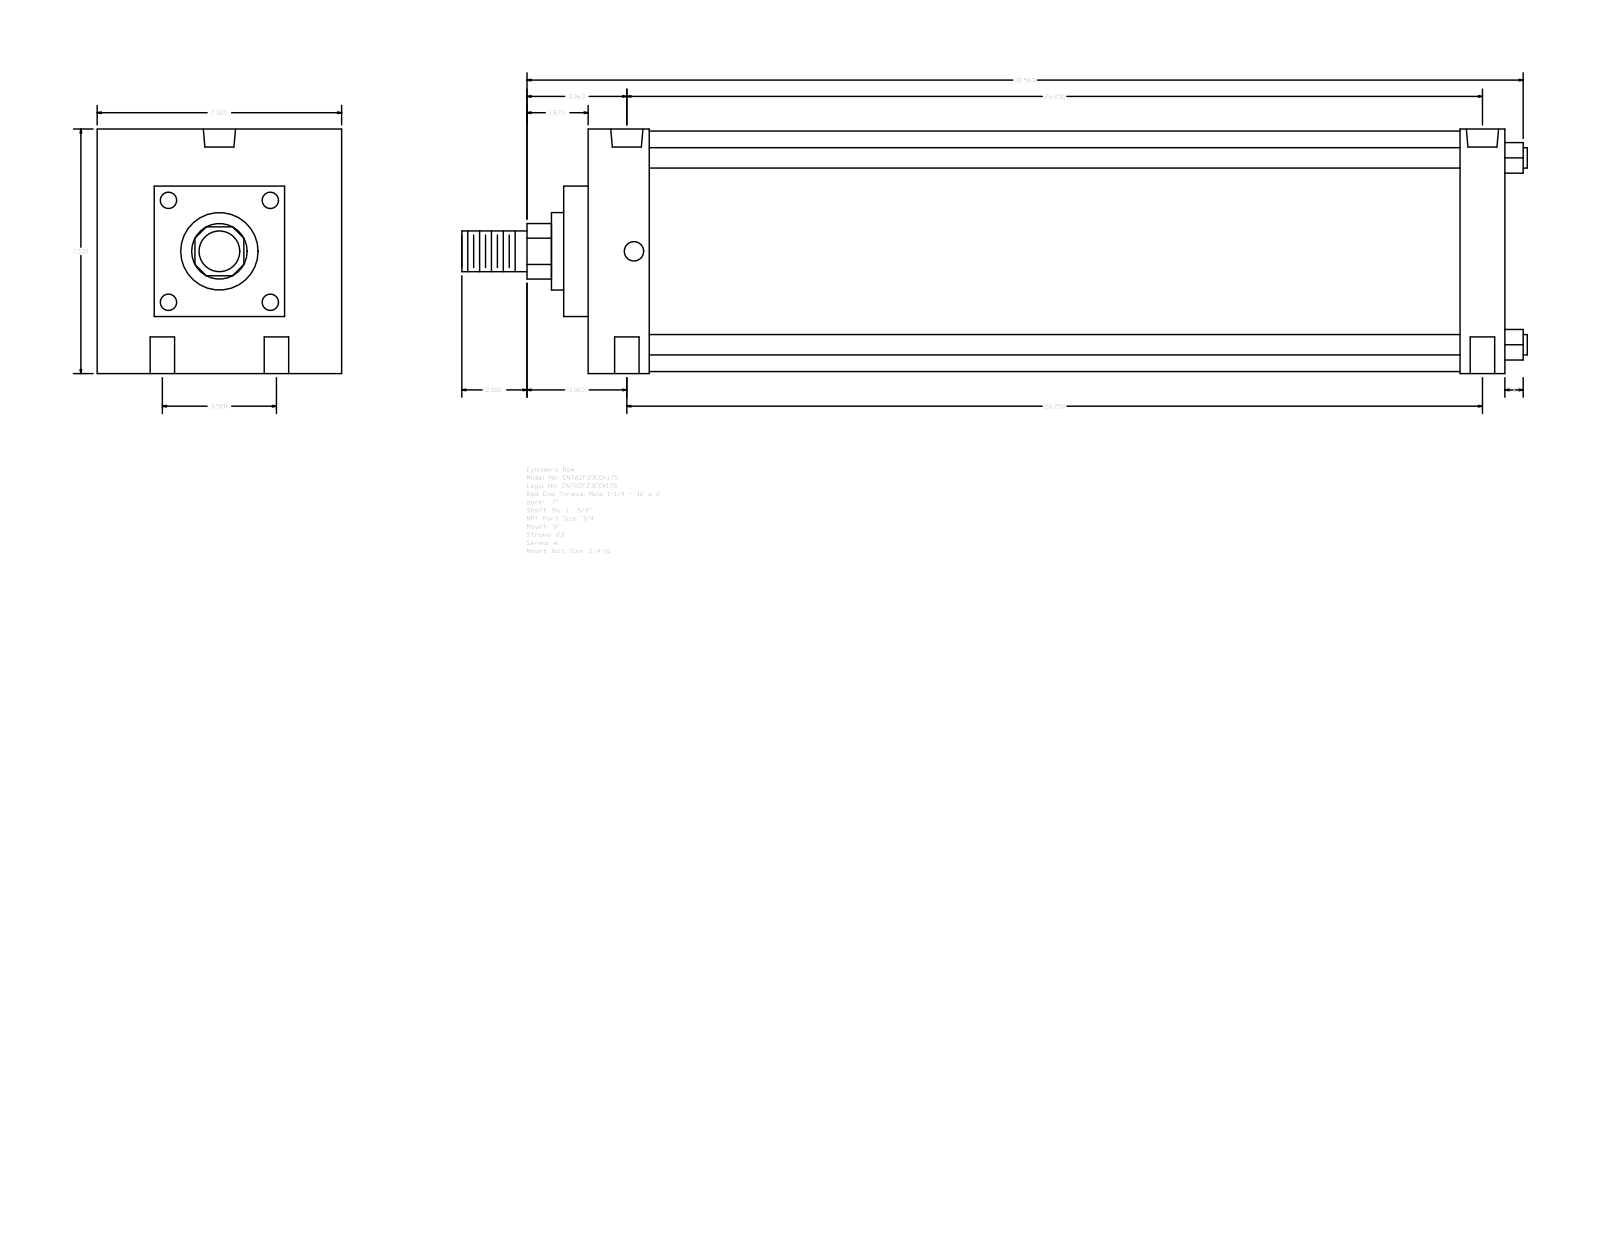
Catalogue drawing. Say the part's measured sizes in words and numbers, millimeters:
The part is named "A_SF__0700_1.75". Its 3-D file was written by "GSSL Pune (CONFIG_CONTROL_DESIGN)". It is 0 solids with 93 faces: 67 planar, 26 cylindrical and 0 other. Overall it measures 830.26 by 190.5 by 190.5 millimeters. Round holes: 4 of diameter 19.05, 2 of diameter 15.08, 2 of diameter 25.12. Round bosses or shafts: 4 of diameter 15.88, 1 of diameter 187.32, 1 of diameter 60.33, 1 of diameter 44.45, 1 of diameter 31.75. Partial cylindrical surfaces (rounded edges, fillets, slot ends): 1 of radius 21.63. The main face-to-face distances are 190.5, 714.38, 146.05, 19.05, 47.63, 679.46, 631.83, 666.75, 34.92, 44.45. The hole center spacings are 44.45, 668.23, 666.75, 88.9, 672.65, 655.63.
